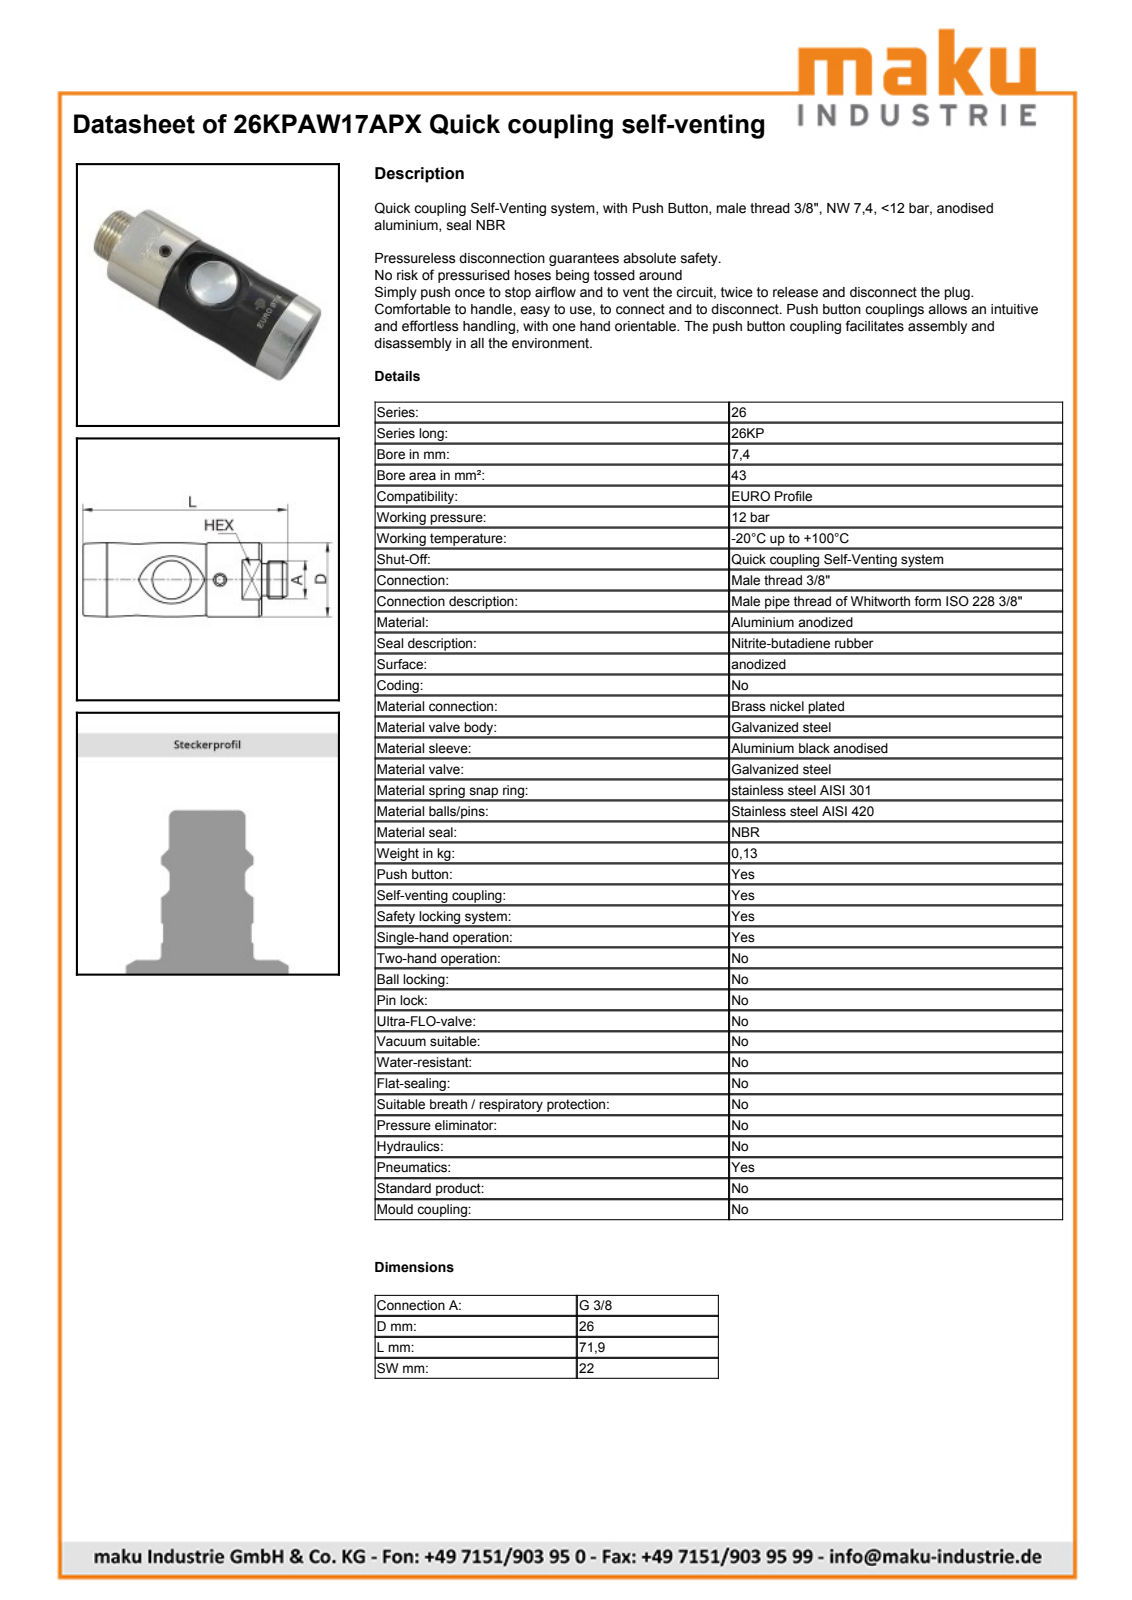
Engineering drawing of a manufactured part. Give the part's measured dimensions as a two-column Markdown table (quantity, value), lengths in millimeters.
| quantity | value |
| --- | --- |
| part name | 26KPAW17APX |
| STEP written by | Autodesk Inventor 2019 (AUTOMOTIVE_DESIGN) |
| units | millimeters |
| bodies | 39 solids, 263 faces (76 planar, 84 cylindrical, 103 other) |
| overall size | 71.9 × 26 × 26 |
| volume | 40 363 mm³ |
| surface area | 26 556 mm² |
| round holes (diameter × count) | 12.4 × 2, 3.5 × 1, 6.5 × 1, 7 × 1, 9.65 × 1, 10.1 × 1, 10.6 × 1, 12.05 × 1, 12.1 × 1, 12.25 × 1, 12.8 × 1, 13.6 × 1 |
| round bosses / shafts (diameter × count) | 26 × 1, 22 × 1, 21.47 × 1, 20.5 × 1, 18.1 × 1, 17.8 × 1, 16.66 × 1, 16.57 × 1 |
| partial cylindrical surfaces (radius × count) | 6.2 × 2, 4.4 × 1 |
| main face-to-face distances | 8.4, 43.4, 35, 42.1, 7.1, 1.3, 19.5, 54.5, 61.6, 62.9 |
| hole center spacings | 0.6, 0.7, 1.3, 17.05 |
